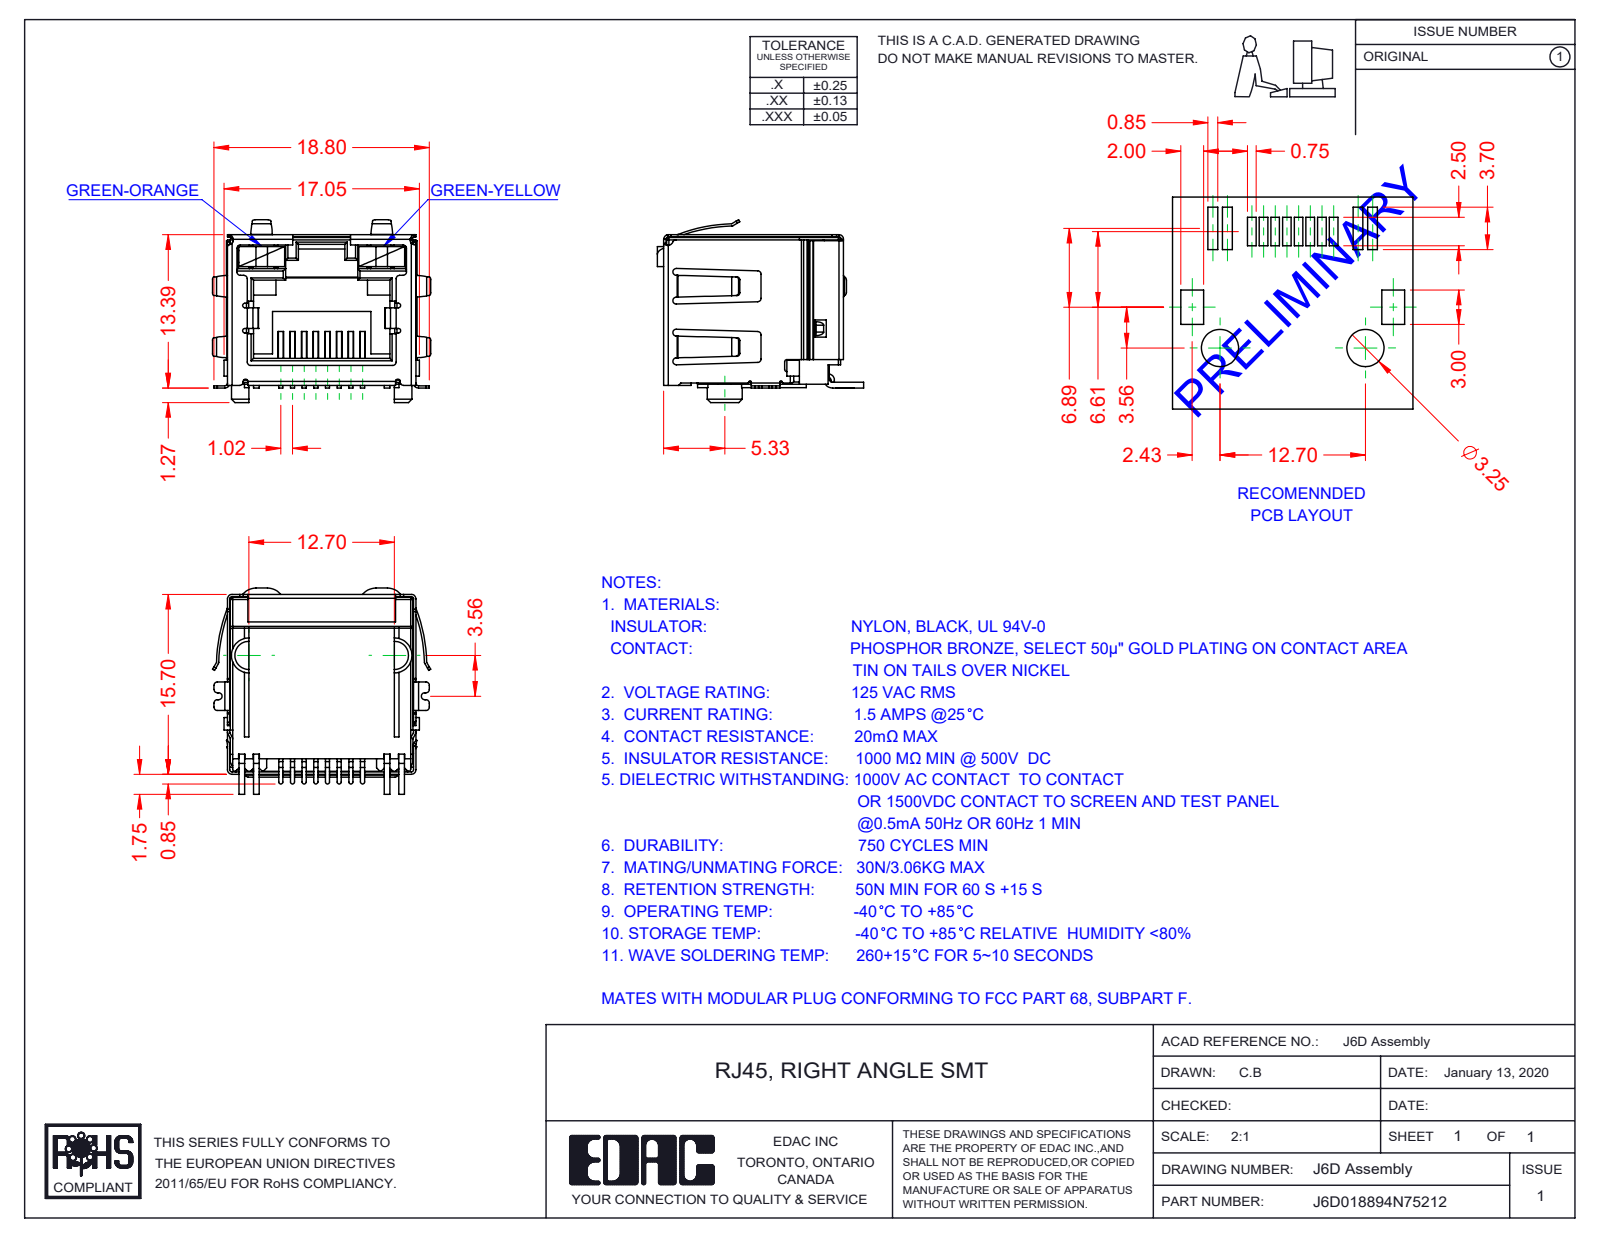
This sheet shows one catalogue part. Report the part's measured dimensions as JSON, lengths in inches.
{"part_name": "6D LED RH_5-Green-Yellow; 6D LED LH_7-Green-Orange; J6D018894N75212; 6D Shield_LED - EMI (+2 more)", "step_written_by": "SolidWorks 2016 (CONFIG_CONTROL_DESIGN)", "units": "inches", "bodies": {"solids": 12, "faces": 1034, "planar": 703, "cylindrical": 286, "other": 45}, "overall_size": [0.75, 0.709, 0.628], "volume_in3": 0.109, "surface_area_in2": 7.434, "partial_cylinders_radius": [[0.012, 55], [0.008, 40], [0.016, 19], [0.01, 16], [0.004, 12], [0.006, 8], [0.007, 8], [0.02, 6]], "face_to_face_distances": [0.63, 0.638, 0.64, 0.089, 0.039, 0.628, 0.504, 0.018, 0.514, 0.417]}
